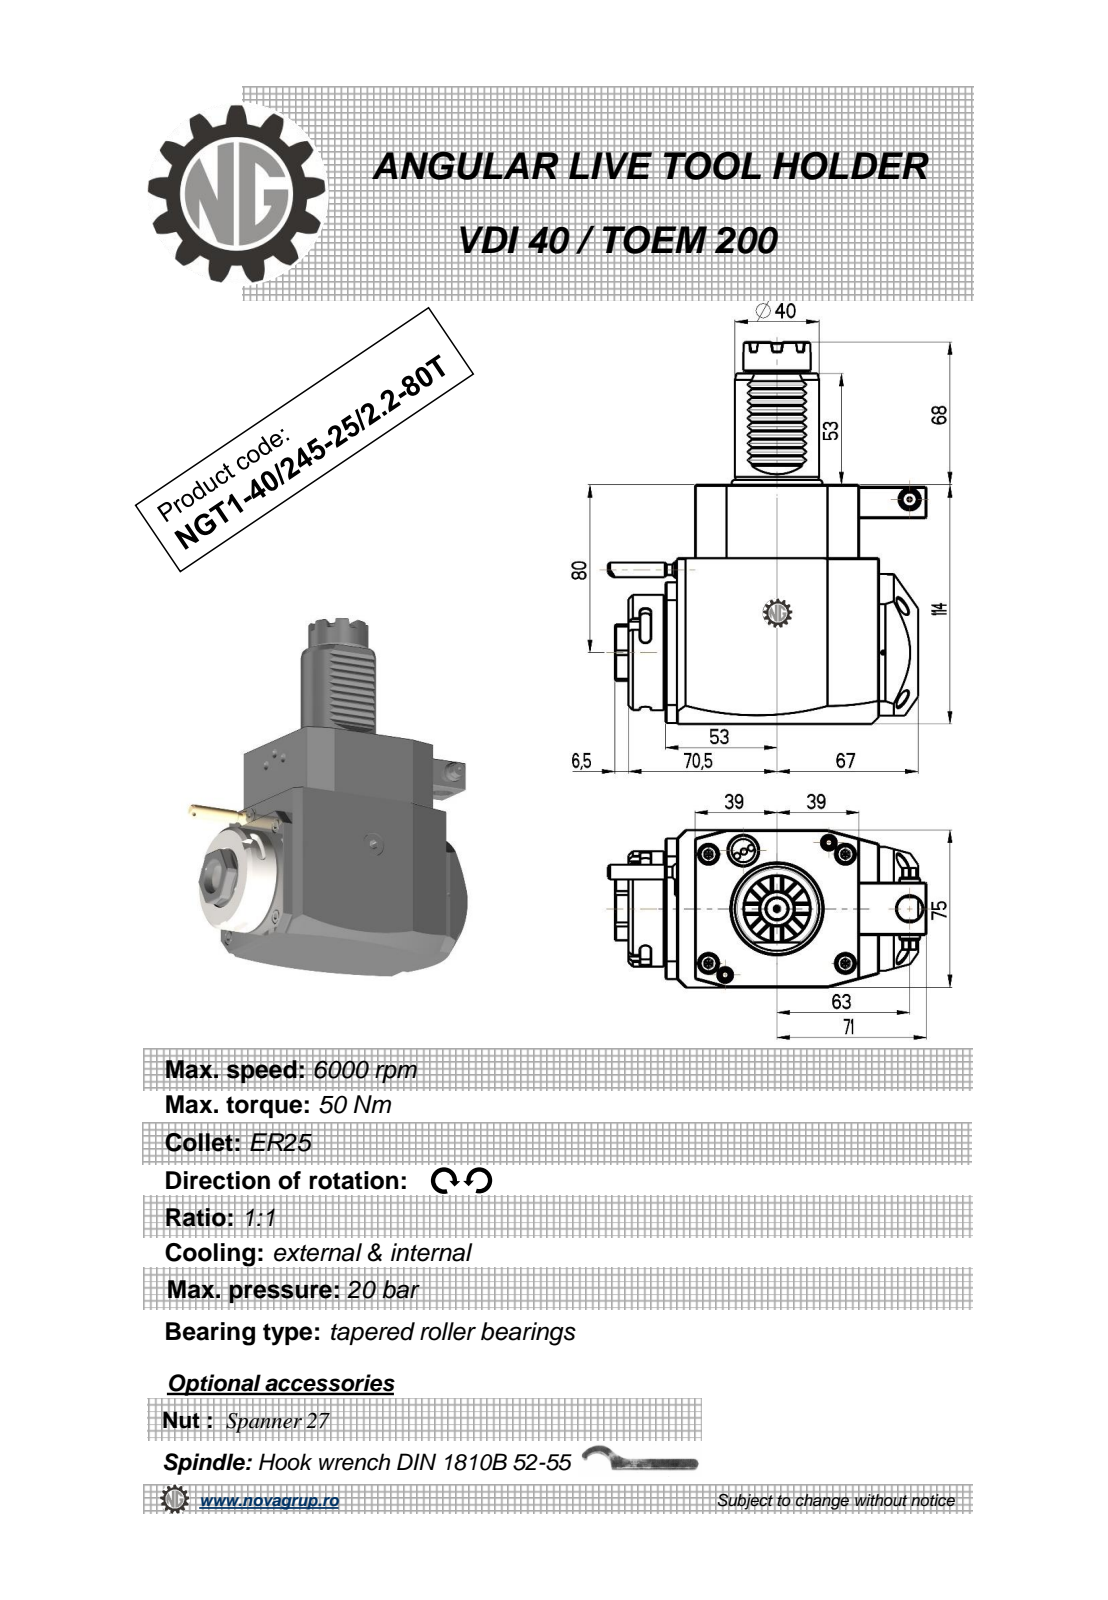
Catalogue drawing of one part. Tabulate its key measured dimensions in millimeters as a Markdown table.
| quantity | value |
| --- | --- |
| part name | NGT1_40_245_25_1_2_80T |
| STEP written by | PRO/ENGINEER BY PARAMETRIC TECHNOLOGY CORPORATION, 2010280 (CONFIG_CONTROL_DESIGN) |
| units | millimeters |
| bodies | 1 solid, 419 faces (221 planar, 86 cylindrical, 112 other) |
| overall size | 182 × 151.33 × 75 |
| volume | 955 790 mm³ |
| surface area | 71 992 mm² |
| round holes (diameter × count) | 2 × 1, 2.5 × 1, 3 × 1, 9.5 × 1, 12 × 1, 18 × 1 |
| round bosses / shafts (diameter × count) | 8 × 2, 55 × 1, 48 × 1, 40 × 1, 32 × 1, 17.2 × 1, 10 × 1, 7 × 1 |
| partial cylindrical surfaces (radius × count) | 0.3 × 10, 2.5 × 6, 180 × 2, 0.5 × 1, 3.85 × 1, 4.25 × 1, 15 × 1, 24.5 × 1 |
| main face-to-face distances | 75, 114, 14, 17.5, 92, 78, 31.5, 109.5, 4, 28 |
| hole center spacings | 37.35, 43.2, 72.5 |
